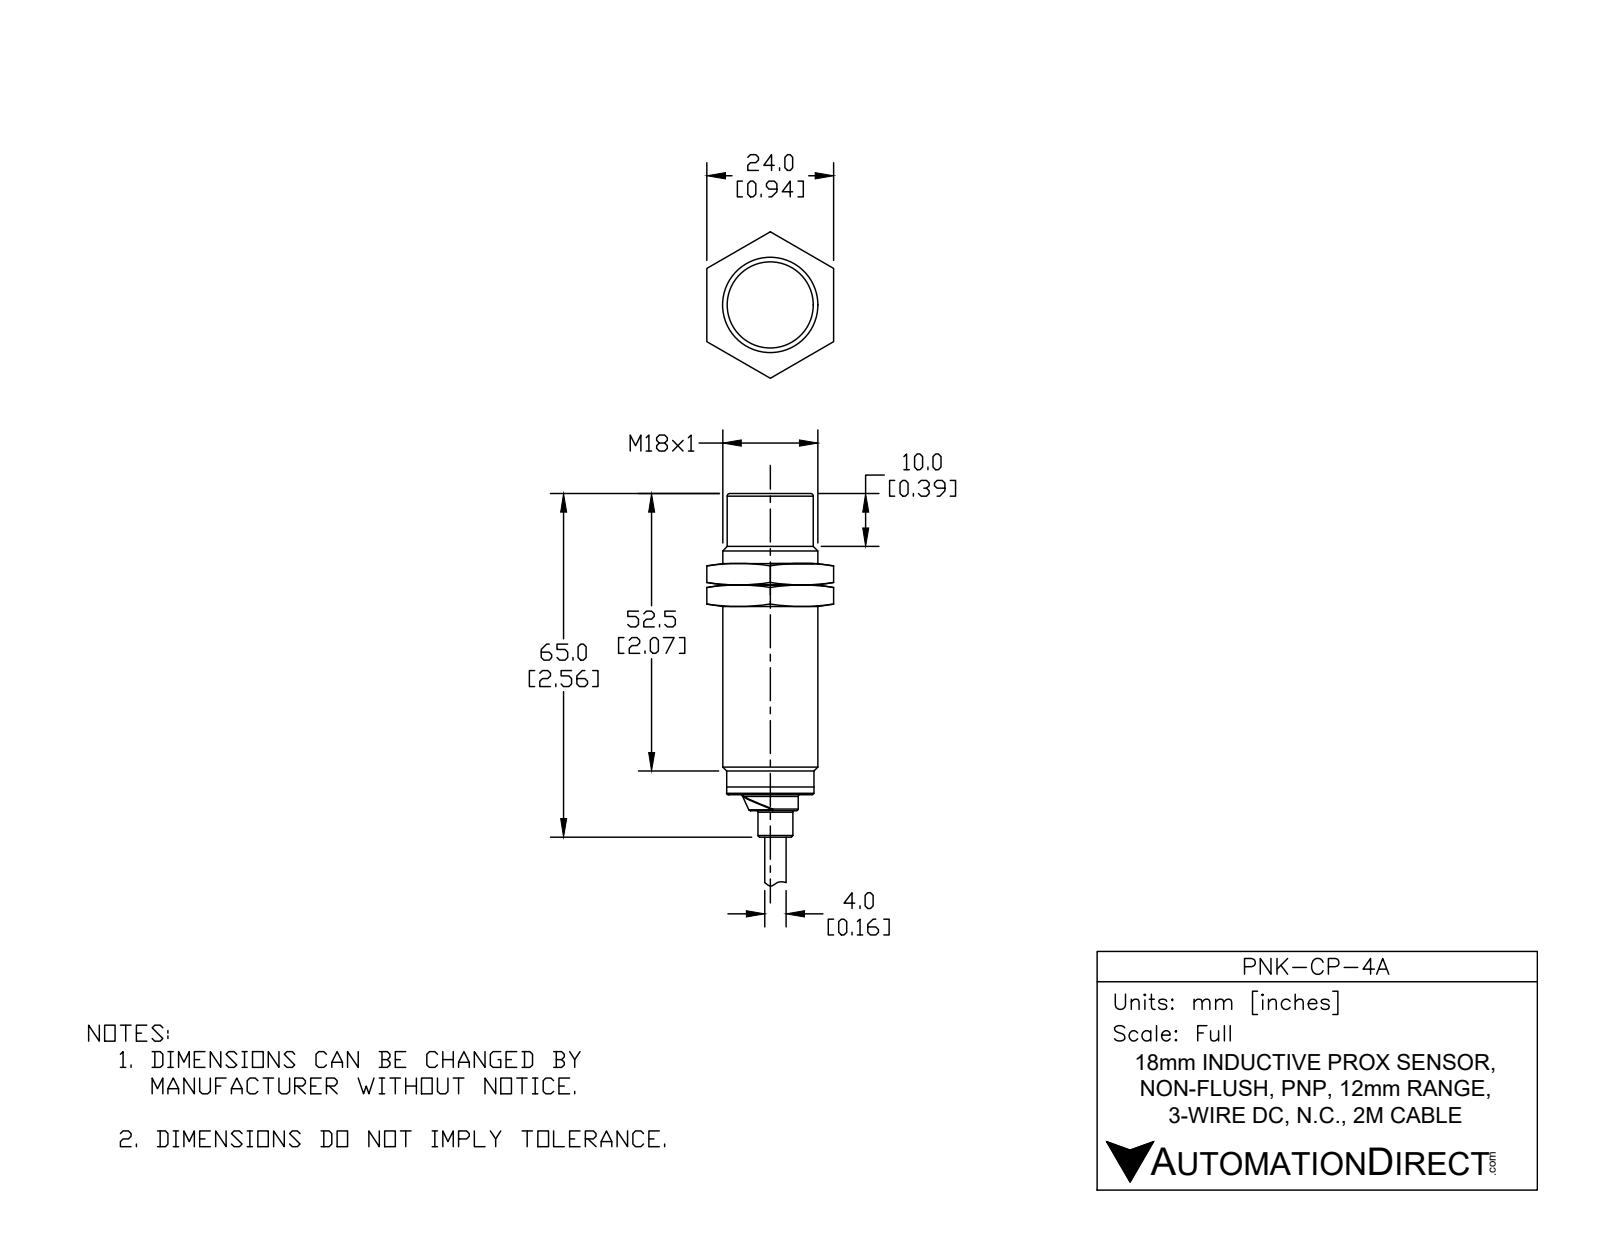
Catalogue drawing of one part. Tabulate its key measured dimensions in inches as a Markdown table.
| quantity | value |
| --- | --- |
| part name | PNK-CP-4A |
| STEP written by | SolidWorks 2017 (AUTOMOTIVE_DESIGN) |
| units | inches |
| bodies | 1 solid, 76 faces (18 planar, 20 cylindrical, 38 other) |
| overall size | 4.559 × 0.709 × 0.709 |
| volume | 0.936 in³ |
| surface area | 7.094 in² |
| round holes (diameter × count) | 0.634 × 1 |
| round bosses / shafts (diameter × count) | 0.709 × 1, 0.65 × 1, 0.65 × 1, 0.633 × 1, 0.417 × 1, 0.26 × 1, 0.157 × 1 |
| partial cylindrical surfaces (radius × count) | 0.079 × 1, 0.081 × 1, 0.091 × 1 |
| main face-to-face distances | 2.244, 2.362, 0.118, 2.559, 0.315, 0.197, 4.559, 2.315, 2.197, 2 |
